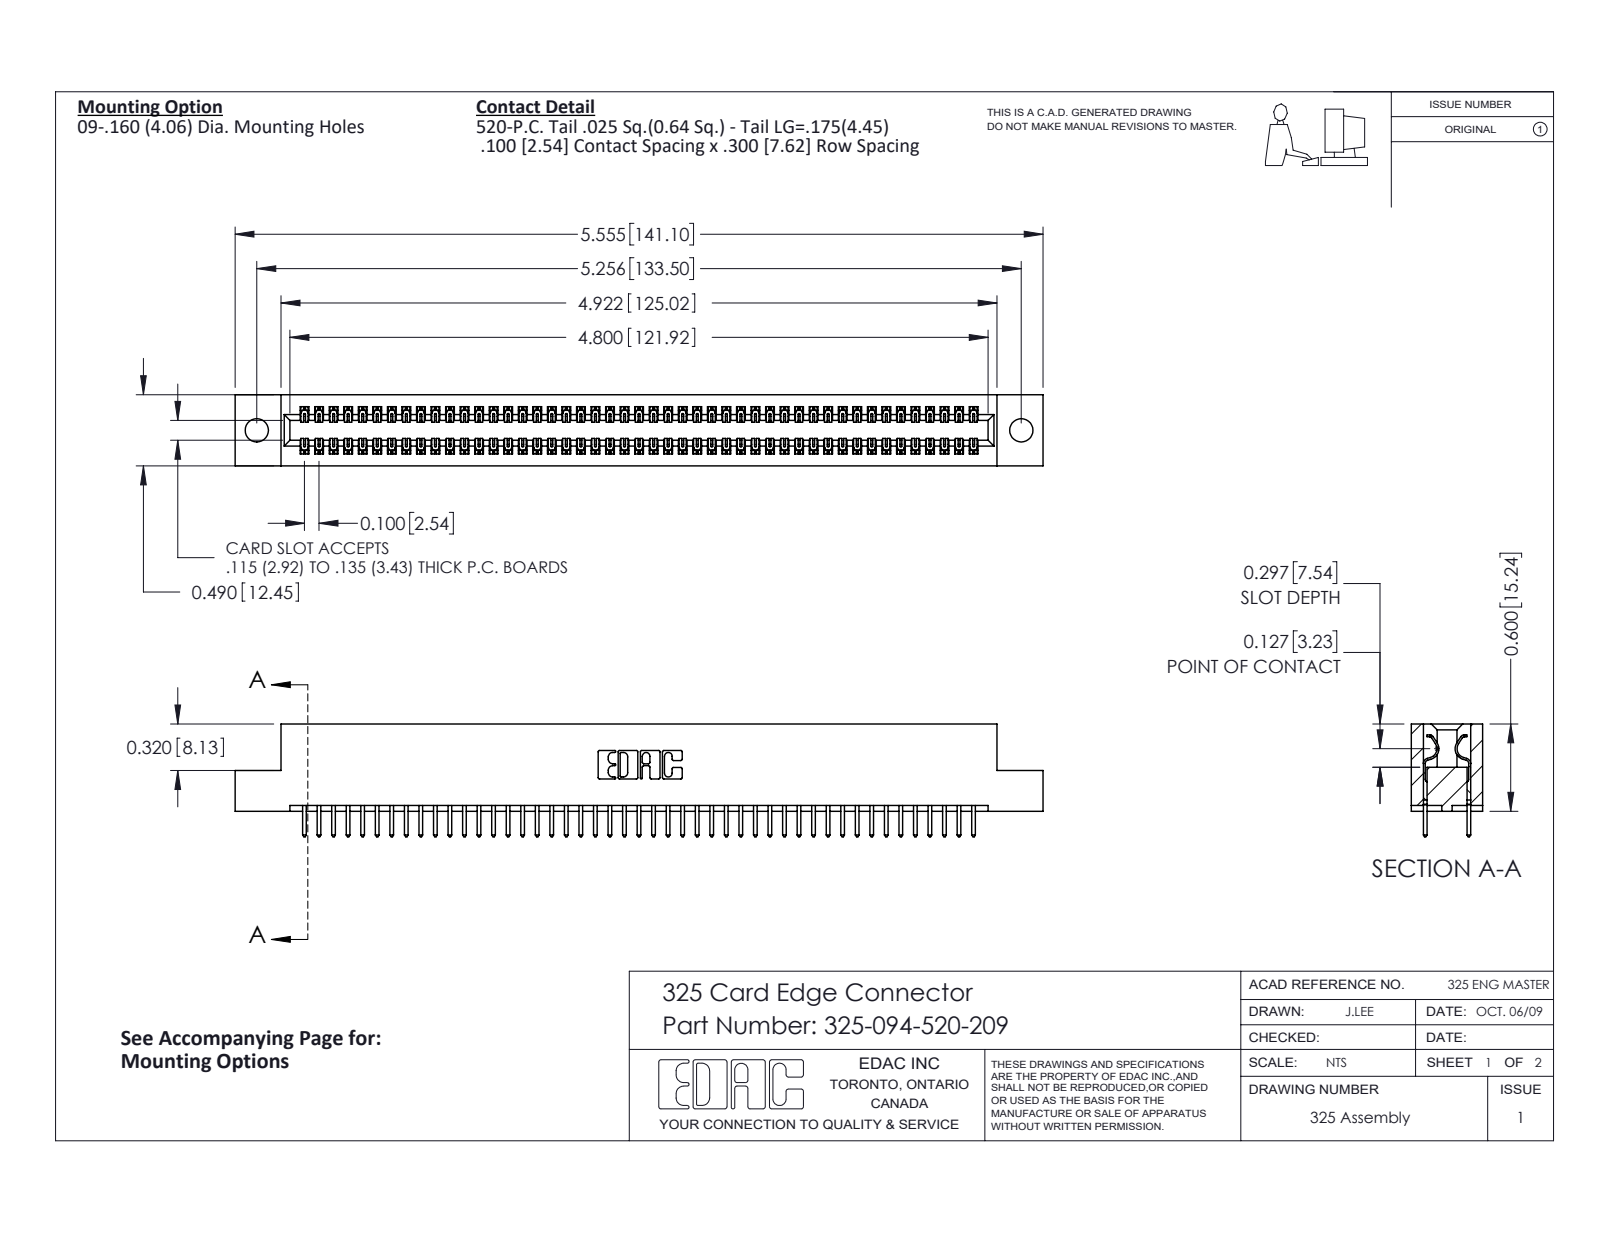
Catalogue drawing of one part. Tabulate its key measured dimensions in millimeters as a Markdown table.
| quantity | value |
| --- | --- |
| part name | 325 Part_.160 TH; 325-292-001_325-293-120; 325-094-520-209 |
| STEP written by | SolidWorks 2016 (CONFIG_CONTROL_DESIGN) |
| units | millimeters |
| bodies | 95 solids, 5002 faces (3454 planar, 1548 cylindrical, 0 other) |
| overall size | 141.1 × 19.7 × 12.4 |
| volume | 18 010 mm³ |
| surface area | 21 650 mm² |
| round holes (diameter × count) | 4.1 × 2 |
| partial cylindrical surfaces (radius × count) | 0.2 × 141, 0.3 × 94, 0.3 × 22, 0.2 × 6, 0.8 × 6, 0.7 × 3, 0.4 × 2, 0.6 × 2 |
| main face-to-face distances | 2.1, 10.3, 7.6, 12.4, 2.7, 9.7, 0.6, 8.3, 7, 14.2 |
| hole center spacings | 133.5 |
